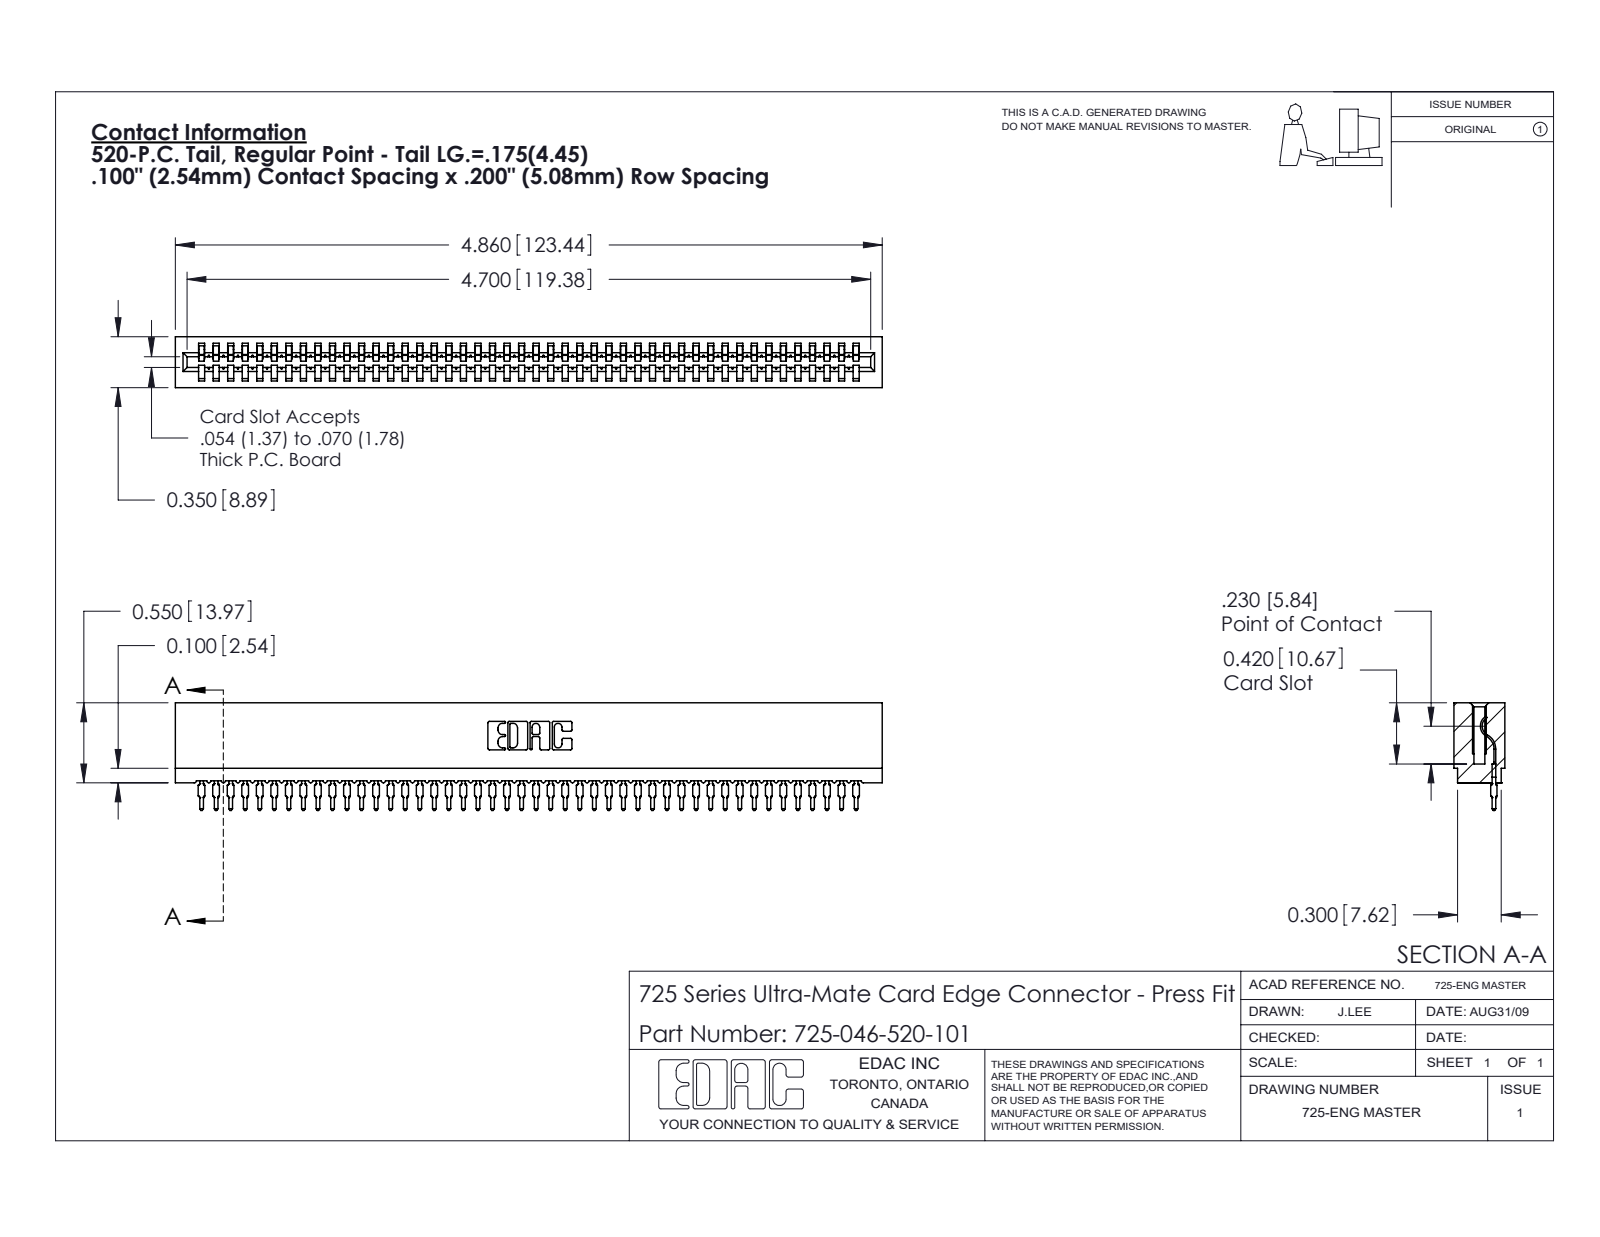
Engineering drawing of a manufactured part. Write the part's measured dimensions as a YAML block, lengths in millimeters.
part_name: "725-046-520-101; 725 Part_Insulator Option - 01; 745-292-001_520"
step_written_by: "SolidWorks 2020 (CONFIG_CONTROL_DESIGN)"
units: millimeters
bodies: {solids: 47, faces: 5247, planar: 3137, cylindrical: 914, other: 1196}
overall_size: [123.4, 18.8, 8.9]
volume: 9280
surface_area: 17670
partial_cylinders:
  - {radius: 0.4, count: 92}
  - {radius: 0.5, count: 92}
  - {radius: 0.3, count: 22}
  - {radius: 0.2, count: 6}
  - {radius: 0.8, count: 6}
  - {radius: 0.1, count: 4}
  - {radius: 0.3, count: 4}
  - {radius: 0.7, count: 3}
face_to_face_distances: [8.9, 5.1, 5.4, 3.5, 2.5, 1.1, 7.7, 2.4, 4.2, 7.6]
